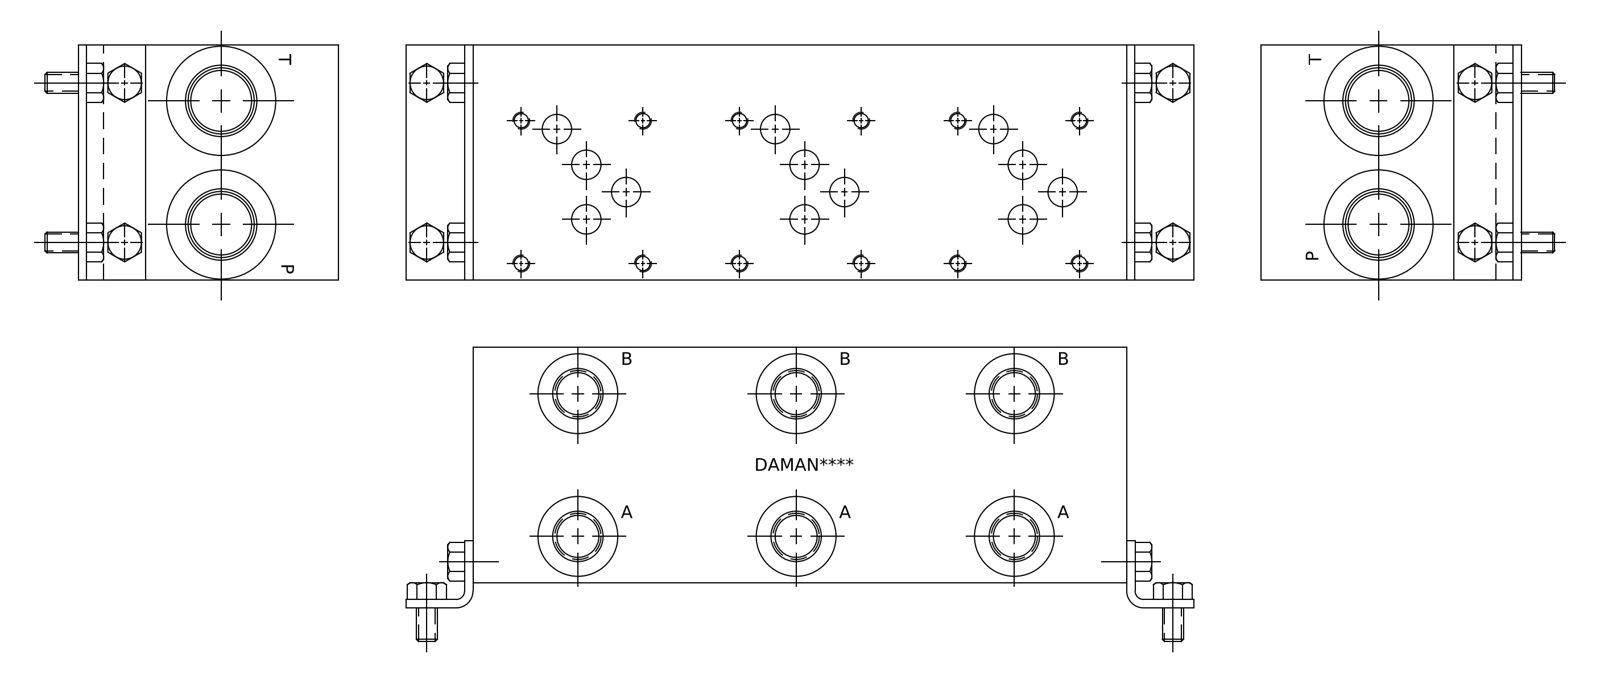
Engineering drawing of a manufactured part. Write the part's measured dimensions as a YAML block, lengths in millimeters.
part_name: "Part_AD05P033S_3D"
step_written_by: "Autodesk Inventor 2020 (CONFIG_CONTROL_DESIGN)"
units: millimeters
bodies: {solids: 1, faces: 736, planar: 393, cylindrical: 94, other: 249}
overall_size: [247.65, 88.9, 88.9]
volume: 1828000
surface_area: 130444
round_holes:
  - {diameter: 5.11, count: 12}
  - {diameter: 6.35, count: 12}
  - {diameter: 11.13, count: 12}
  - {diameter: 15.88, count: 6}
  - {diameter: 17.5, count: 6}
  - {diameter: 19.05, count: 6}
  - {diameter: 19.25, count: 6}
  - {diameter: 30.63, count: 6}
  - {diameter: 6.53, count: 2}
  - {diameter: 7.92, count: 2}
  - {diameter: 23.01, count: 2}
  - {diameter: 24.92, count: 2}
face_to_face_distances: [88.9, 0.79, 247.65, 246.86, 88.11, 246.07, 19.05, 19.84, 227.81, 227.02]
hole_center_spacings: [82.55, 98.63, 165.1, 46.05, 70.95, 53.98, 18.27, 29.74]
